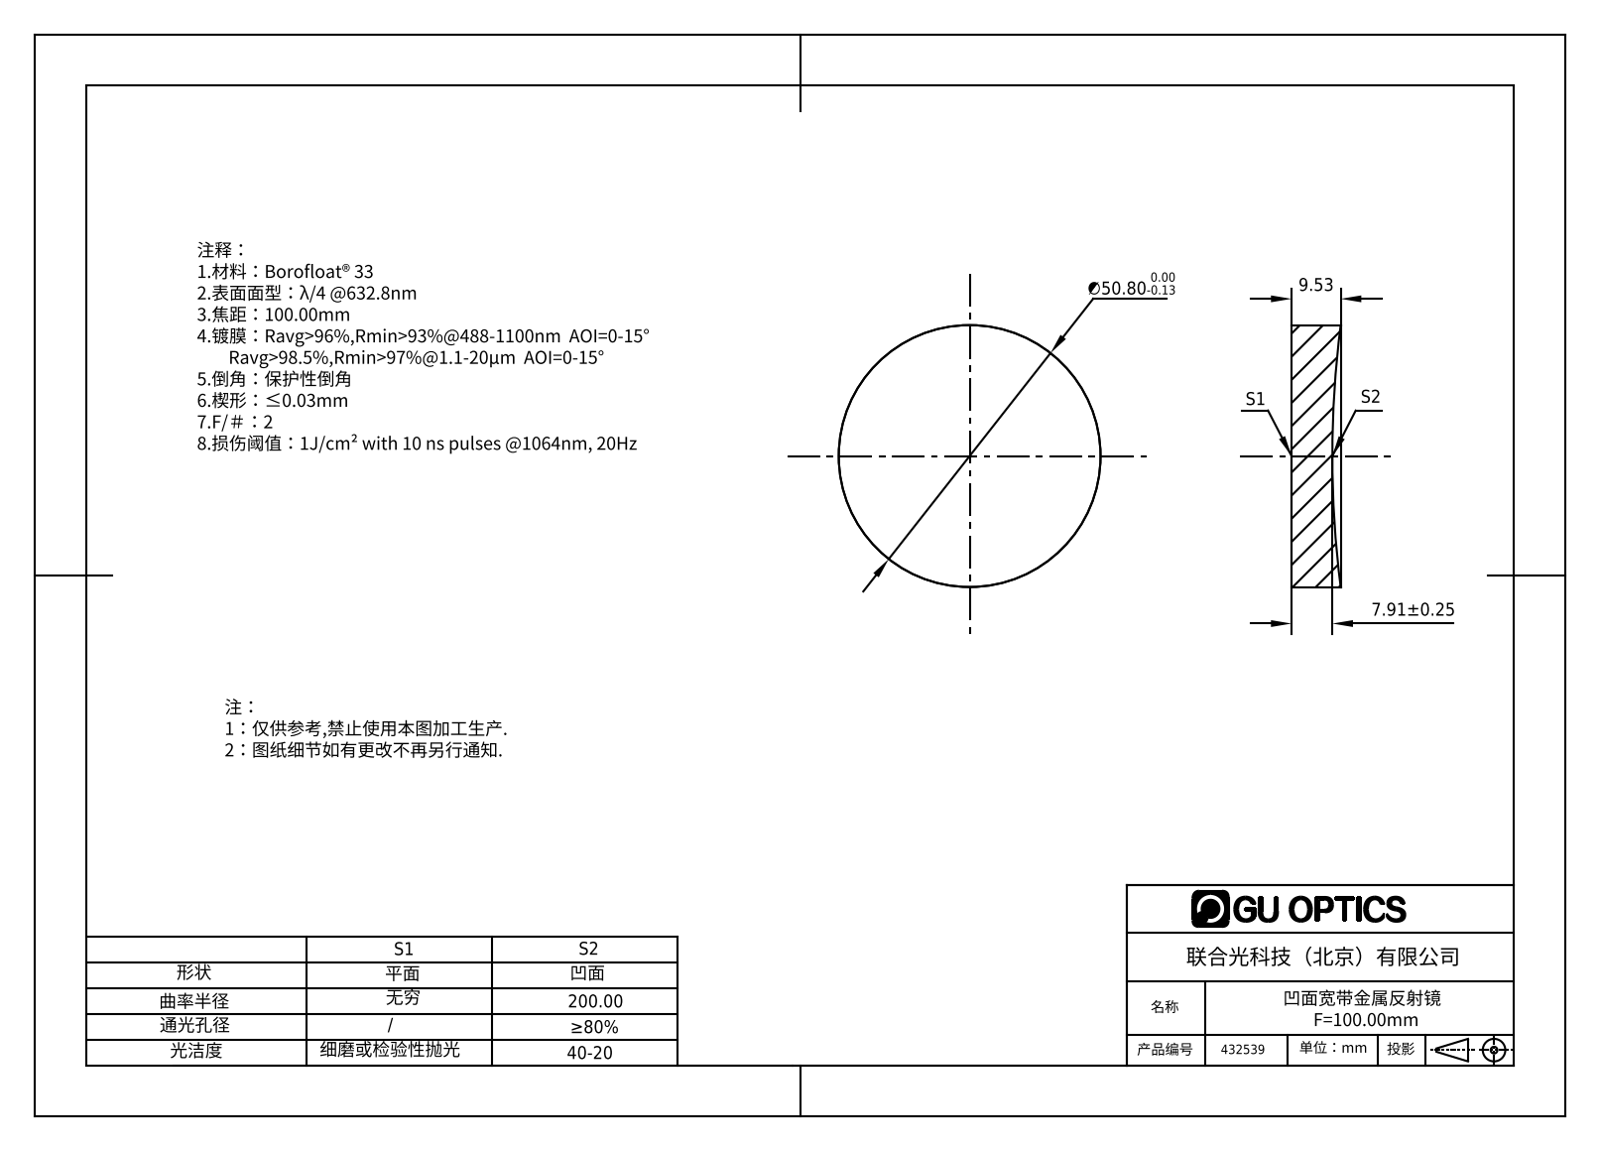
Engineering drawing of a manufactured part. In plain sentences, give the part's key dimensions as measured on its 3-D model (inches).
The part is named "432531". Its 3-D file was written by "SolidWorks 2016 (AUTOMOTIVE_DESIGN)". It is 1 solid with 5 faces: 1 planar, 2 cylindrical and 2 other. Overall it measures 2 by 2 by 0.375 inches. Its volume is 1.078 cubic inches and its surface area 8.654 square inches. Round bosses or shafts: 1 of diameter 2.
